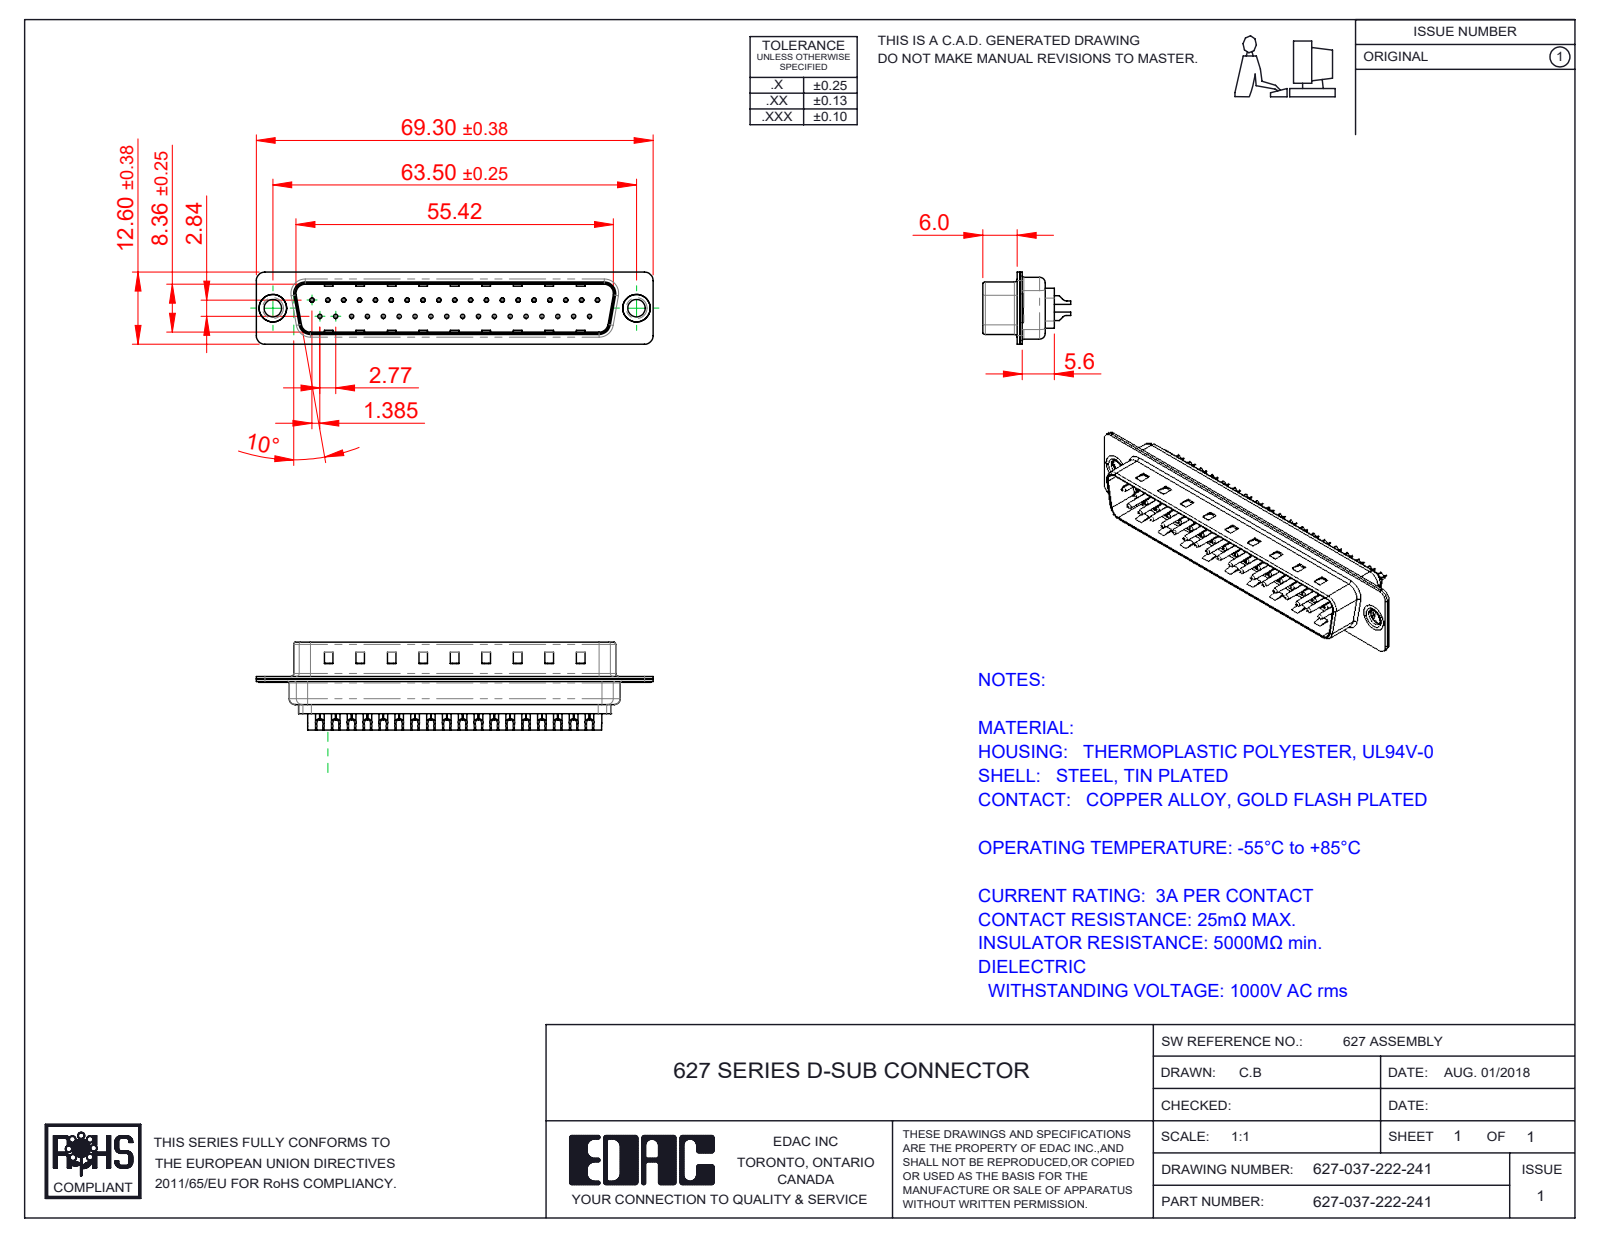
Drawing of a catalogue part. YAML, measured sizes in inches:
part_name: "627 Shell Rear_37 Contacts; 627 Housing_37 LP; 627-037-222-041; 627 Shell Front_37 Contacts (+3 more)"
step_written_by: "SolidWorks 2020 (CONFIG_CONTROL_DESIGN)"
units: inches
bodies: {solids: 42, faces: 2754, planar: 721, cylindrical: 1198, other: 835}
overall_size: [2.728, 0.604, 0.496]
volume: 0.222
surface_area: 16.45
round_holes:
  - {diameter: 0.014, count: 37}
  - {diameter: 0.043, count: 37}
  - {diameter: 0.063, count: 37}
  - {diameter: 0.12, count: 2}
  - {diameter: 0.157, count: 2}
  - {diameter: 0.189, count: 2}
round_bosses_or_shafts:
  - {diameter: 0.079, count: 37}
  - {diameter: 0.059, count: 37}
  - {diameter: 0.03, count: 37}
  - {diameter: 0.197, count: 2}
  - {diameter: 0.193, count: 2}
  - {diameter: 0.14, count: 2}
partial_cylinders:
  - {radius: 0.059, count: 16}
  - {radius: 0.079, count: 12}
  - {radius: 0.02, count: 8}
  - {radius: 0.063, count: 8}
  - {radius: 0.039, count: 6}
  - {radius: 0.01, count: 4}
  - {radius: 0.024, count: 4}
  - {radius: 0.026, count: 4}
face_to_face_distances: [0.016, 0.032, 0.377, 0.018, 0.345, 0.035, 0.059, 0.055, 0.238, 0.02]
hole_center_spacings: [0.124, 0.109, 0.218, 0.327, 0.198, 0.398, 0.436, 0.503]
